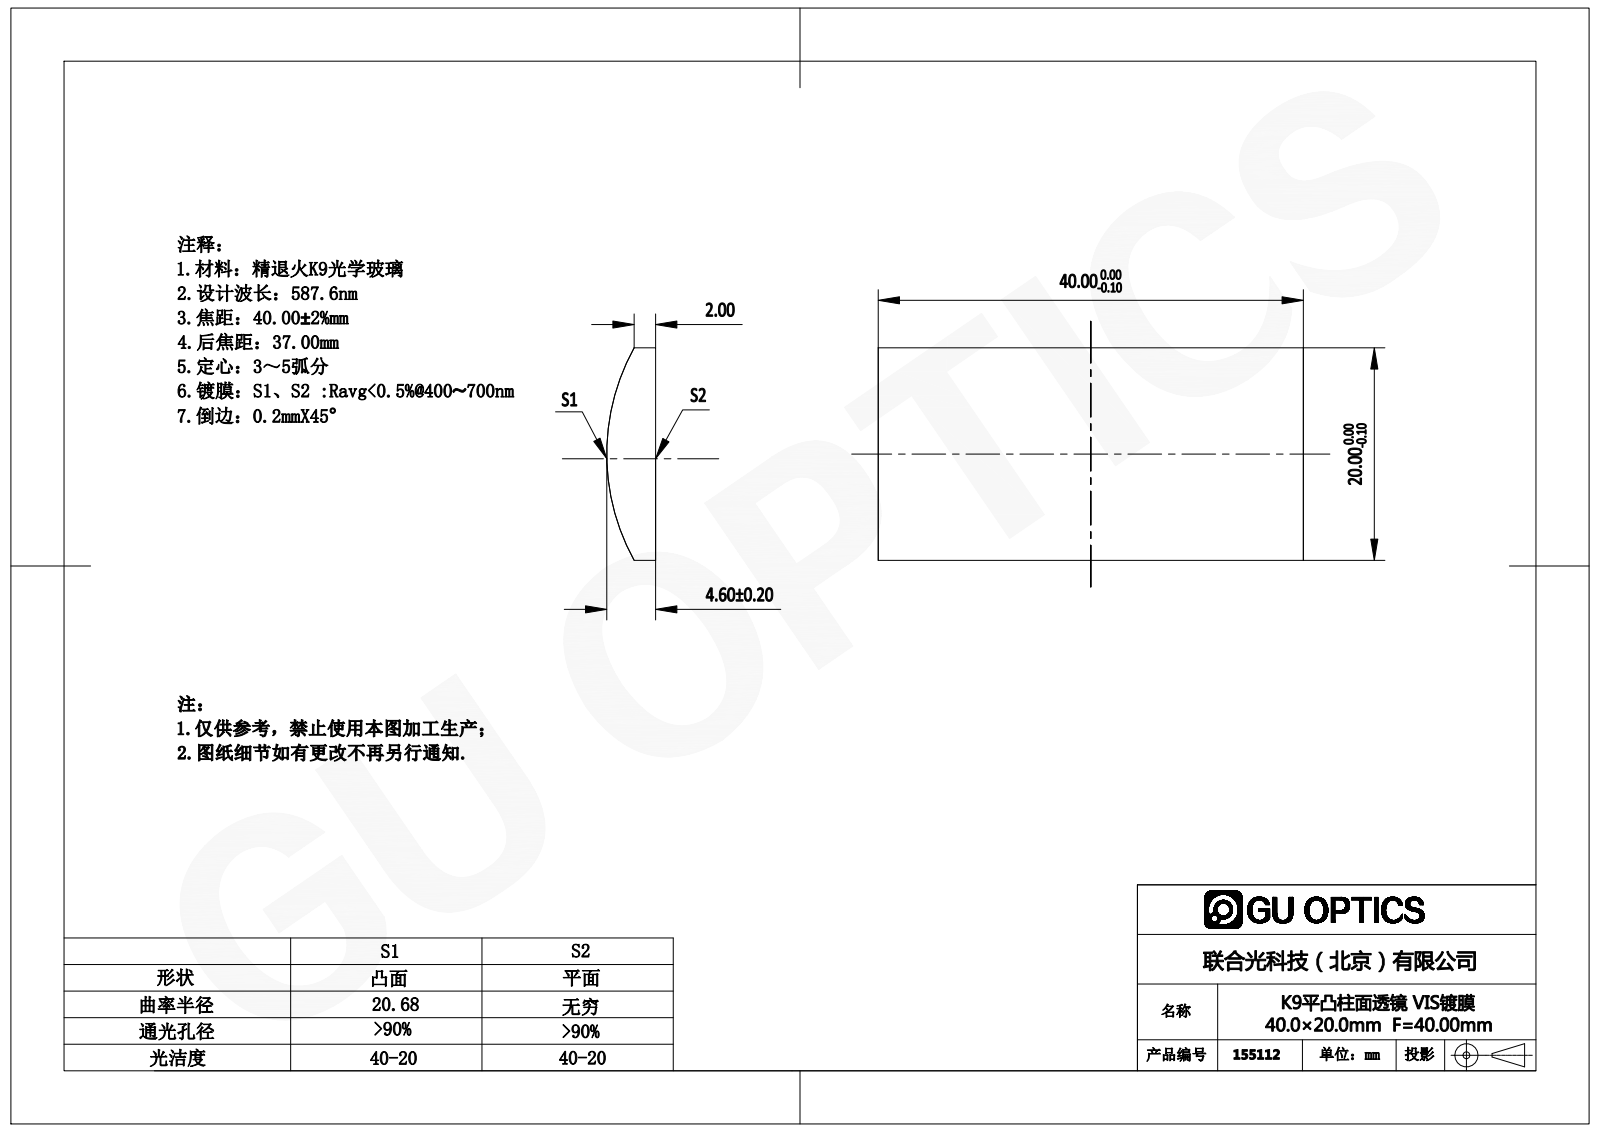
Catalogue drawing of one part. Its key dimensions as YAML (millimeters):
part_name: "155046"
step_written_by: "SolidWorks 2016 (AUTOMOTIVE_DESIGN)"
units: millimeters
bodies: {solids: 1, faces: 6, planar: 5, cylindrical: 1, other: 0}
overall_size: [40, 20, 4.6]
volume: 3011
surface_area: 1947
partial_cylinders:
  - {radius: 20.68, count: 1}
face_to_face_distances: [20, 40]
